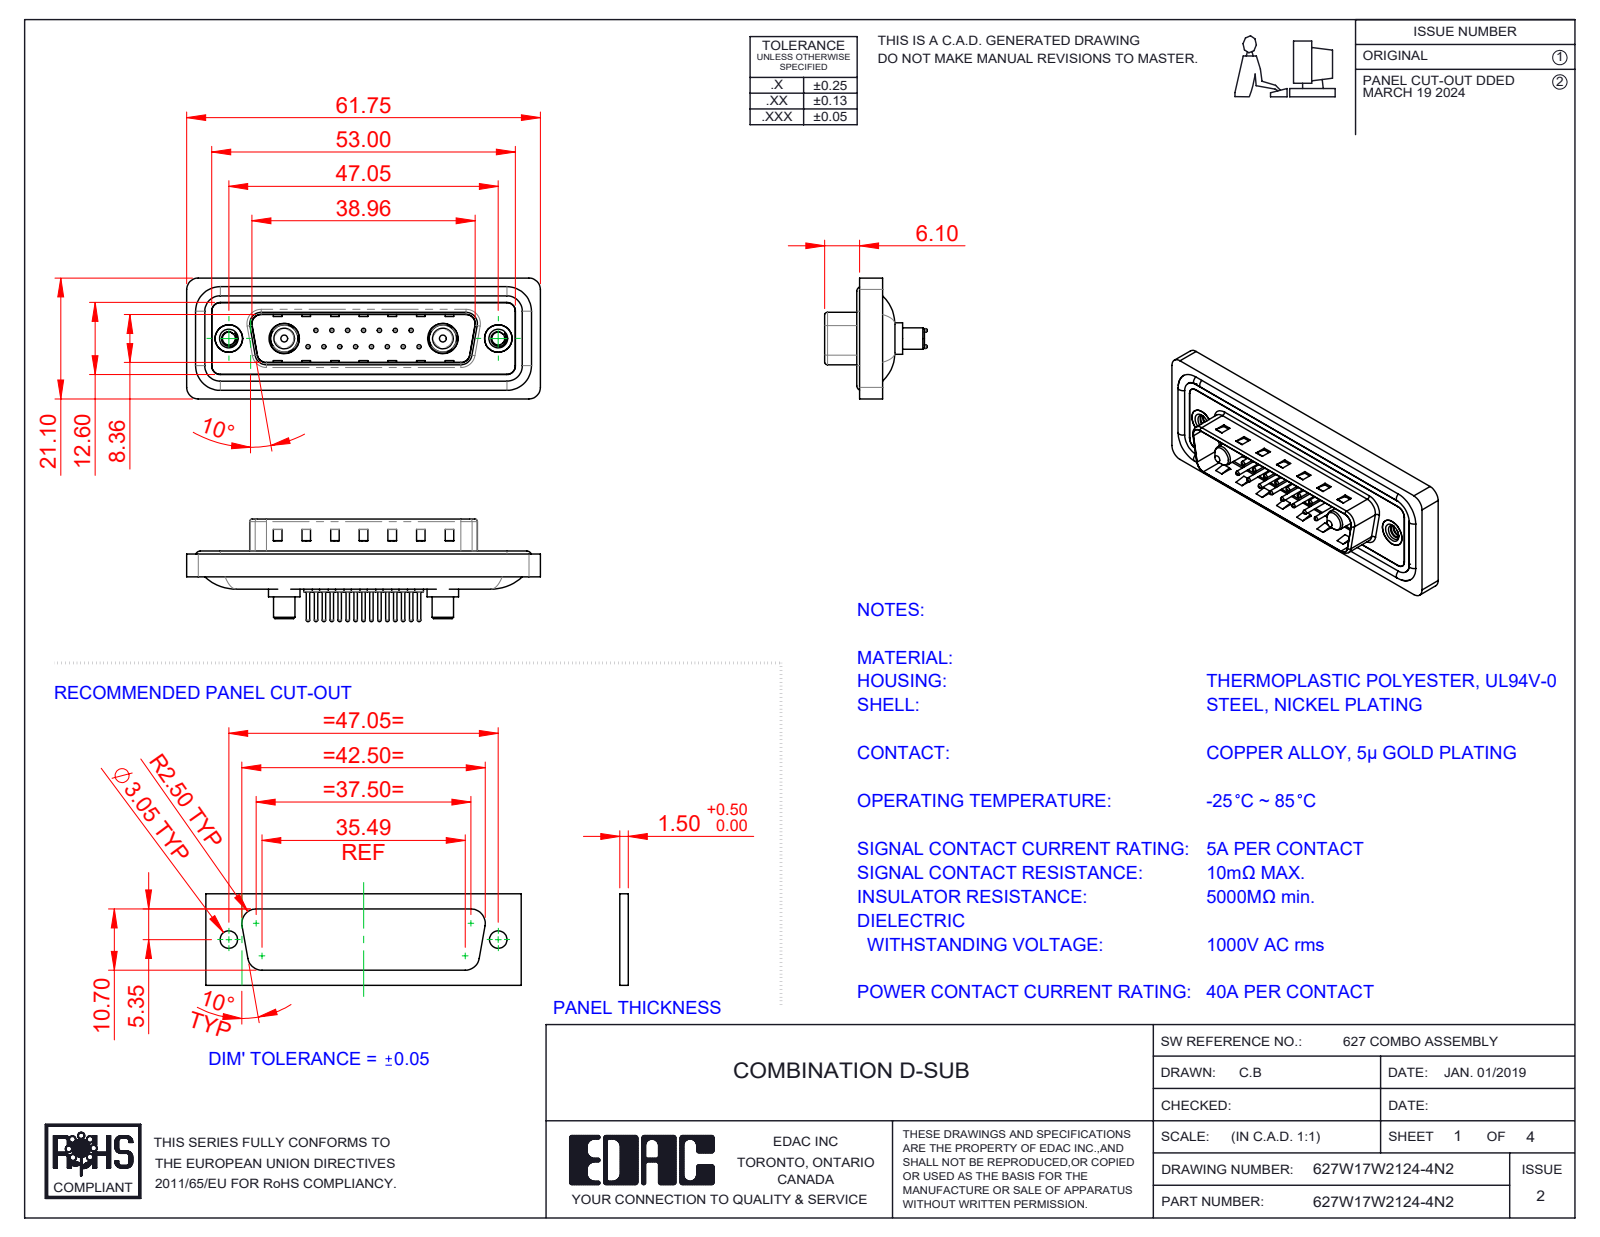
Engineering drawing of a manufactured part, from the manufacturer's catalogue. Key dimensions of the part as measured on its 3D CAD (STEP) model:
Part name (STEP PRODUCT): 627Combo Housing_17W2; 627Combo Threaded Rivet_2; 627Combo Contact Row 2_24; 627Combo Shell Front_25 Contacts (+5 more)
STEP written by: SolidWorks 2023 (CONFIG_CONTROL_DESIGN)
Units: millimetres
Bodies: 26 solids, 1116 faces (334 planar, 436 cylindrical, 346 other)
Overall size (bounding box): 61.75 × 21.1 × 17.9
Volume: 7 303 mm³ · Surface area: 11 936 mm²
Round holes (diameter × count): ⌀0.75 ×15, ⌀1.6 ×15, ⌀2 ×15, ⌀2.26 ×2, ⌀4 ×2, ⌀4.8 ×2, ⌀4.85 ×2, ⌀5 ×2, ⌀5.3 ×2
Round bosses / shafts (diameter × count): ⌀1.5 ×15, ⌀0.6 ×15, ⌀1.6 ×4, ⌀5.5 ×2, ⌀5.2 ×2, ⌀4.9 ×2, ⌀4.75 ×2, ⌀3.75 ×2
Partial cylindrical surfaces — rounded edges, fillets, slot ends (radius × count): R1.5 ×22, R2 ×18, R0.5 ×8, R1.6 ×8, R0.25 ×4, R0.6 ×4, R0.65 ×4, R0.9 ×4
Main face-to-face distances: 0.4, 1.5, 1.1, 1.6, 0.5, 3.1, 2.9, 0.82, 9.58, 4.1
Hole centre spacings: 3.16, 2.77, 5.54, 8.31, 5.04, 7.49, 11.08, 5.03
